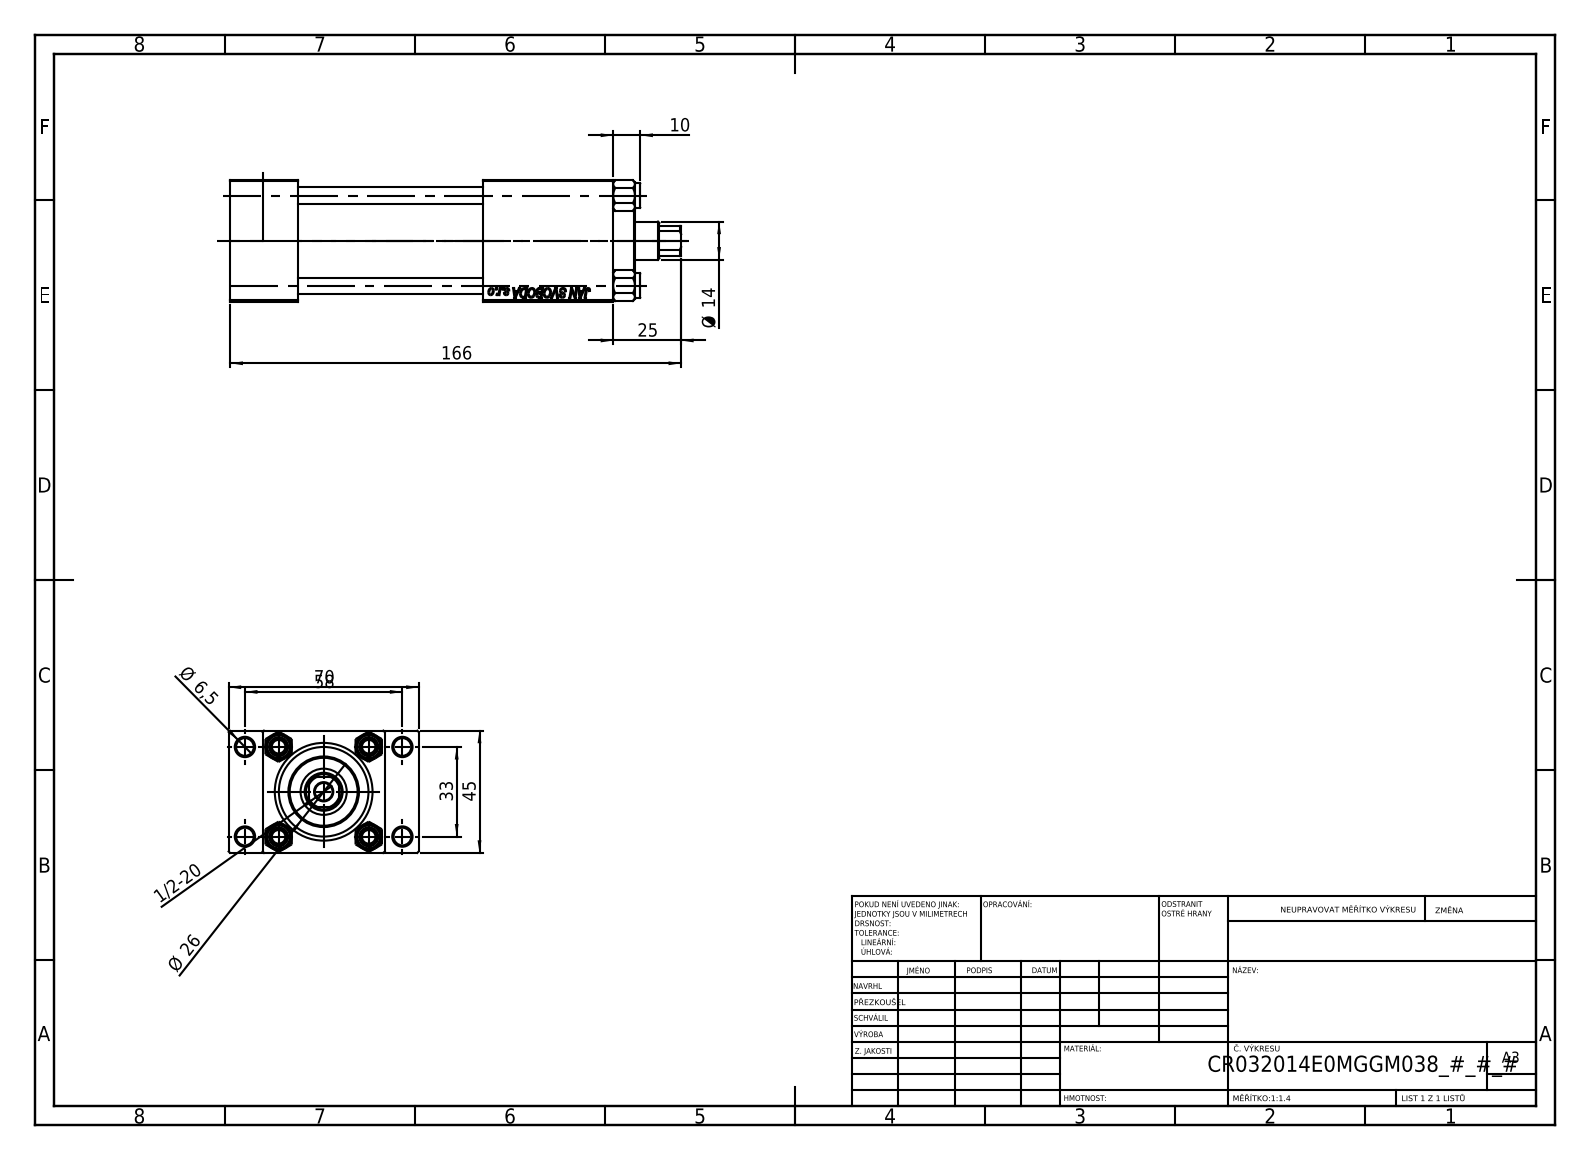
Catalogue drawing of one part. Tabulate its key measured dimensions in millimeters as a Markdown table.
| quantity | value |
| --- | --- |
| part name | NUT_M5_E; V215CR_TYCINKA_E; V215_VC_A; V215CR_E_Body (+1 more) |
| STEP written by | SolidWorks 2019 (CONFIG_CONTROL_DESIGN) |
| units | millimeters |
| bodies | 11 solids, 1136 faces (497 planar, 87 cylindrical, 552 other) |
| overall size | 166 × 70 × 45 |
| volume | 230 817 mm³ |
| surface area | 82 180 mm² |
| round holes (diameter × count) | 6.5 × 5, 6 × 4, 7 × 2, 13.16 × 2, 20 × 2, 14 × 1, 17 × 1, 24 × 1, 32 × 1, 33 × 1 |
| round bosses / shafts (diameter × count) | 9 × 4, 38 × 1, 26 × 1 |
| partial cylindrical surfaces (radius × count) | 6.5 × 1 |
| main face-to-face distances | 45, 25, 12.5, 57.5, 141, 116, 70, 93, 68, 48 |
| hole center spacings | 12.4, 23.48, 33.2, 33.37, 35.35, 45.6, 56.35, 33 |
